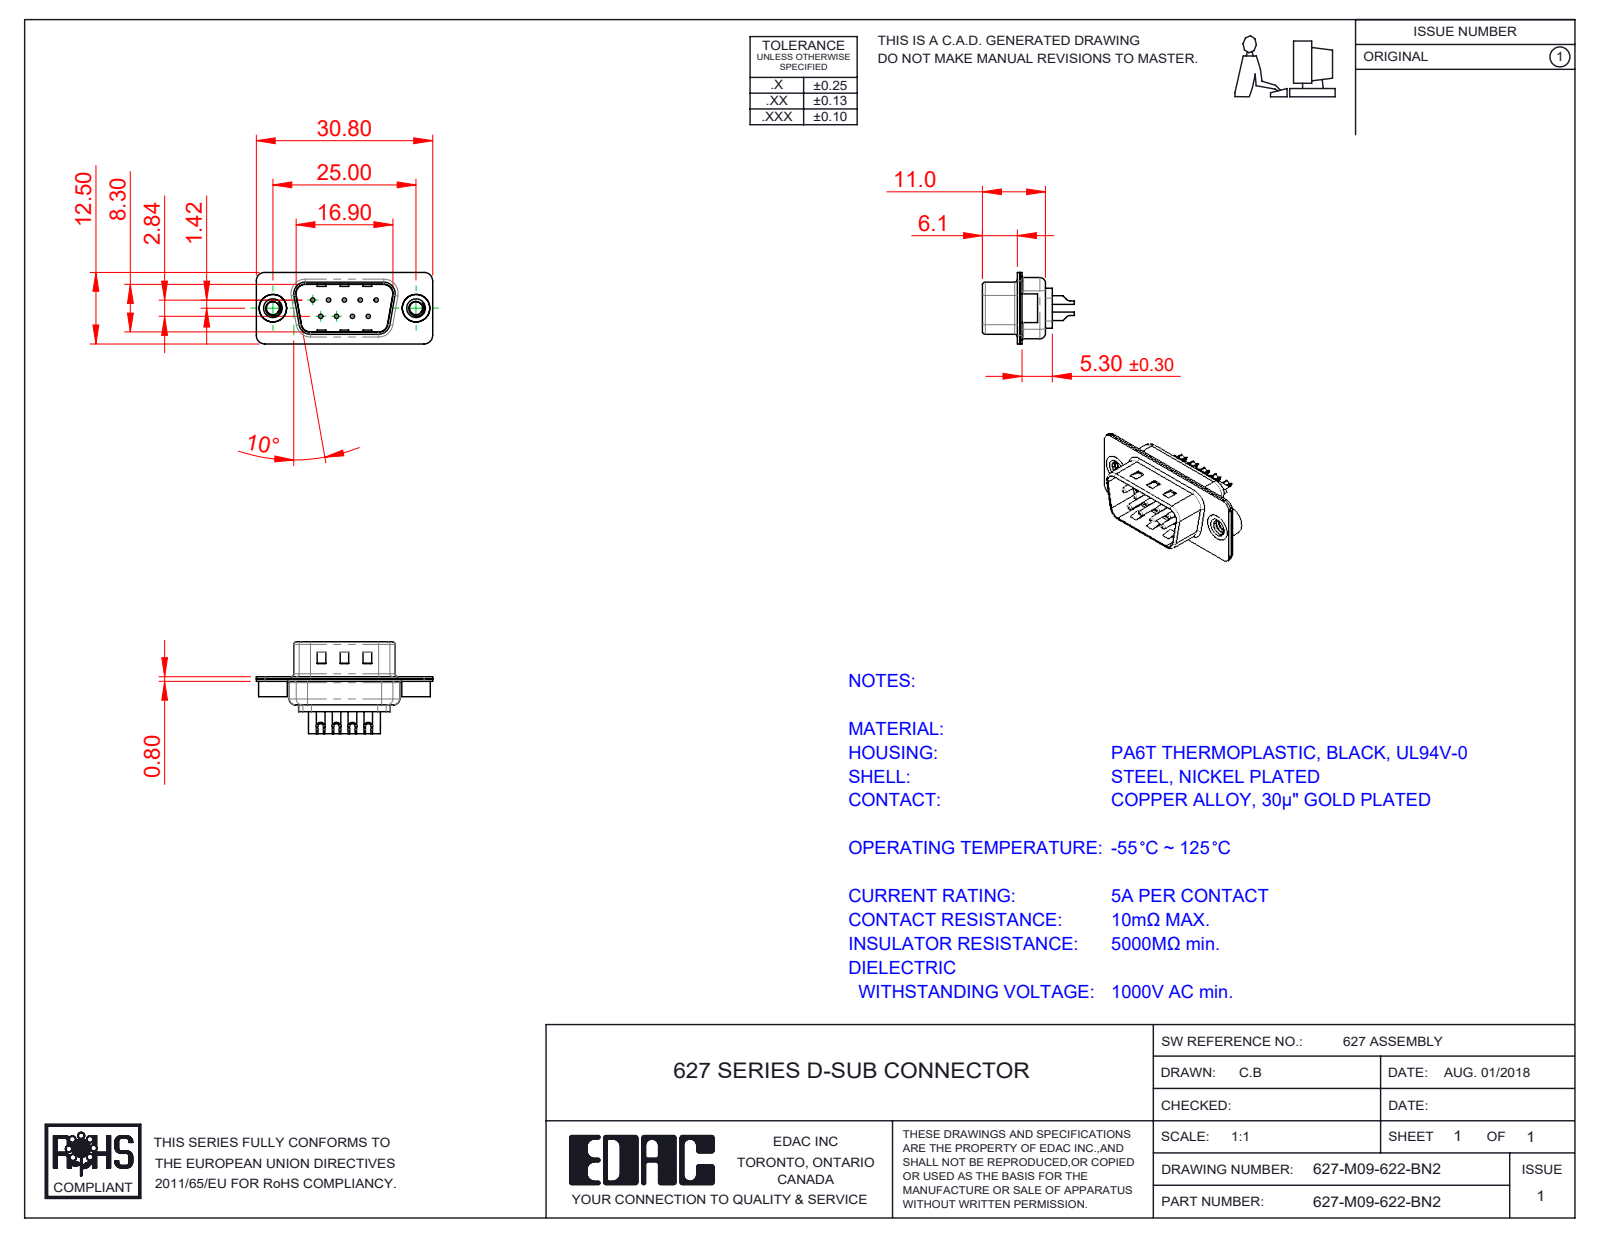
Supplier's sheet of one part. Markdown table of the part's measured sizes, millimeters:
| quantity | value |
| --- | --- |
| part name | 627M Shell Rear_09 Contacts; 627-M09-622-BN2; 627M Contact Row 2_22; 627M Shell Front_09 Contacts (+3 more) |
| STEP written by | SolidWorks 2020 (CONFIG_CONTROL_DESIGN) |
| units | millimeters |
| bodies | 14 solids, 637 faces (188 planar, 273 cylindrical, 176 other) |
| overall size | 30.8 × 16.05 × 12.5 |
| volume | 1 331 mm³ |
| surface area | 3 658 mm² |
| round holes (diameter × count) | 0.75 × 9, 1 × 9, 1.6 × 9, 2 × 9, 2.26 × 2, 4 × 2, 4.8 × 2 |
| round bosses / shafts (diameter × count) | 1.5 × 9, 5 × 2, 4.9 × 2 |
| partial cylindrical surfaces (radius × count) | 1.5 × 16, 2 × 12, 0.5 × 8, 1.6 × 8, 1 × 6, 0.25 × 4, 0.6 × 4, 0.65 × 4 |
| main face-to-face distances | 0.4, 0.8, 9.5, 9.1, 8.7, 0.65, 9.9, 1.2, 0.75, 0.35 |
| hole center spacings | 3.16, 2.77, 5.54, 5.03, 5.04, 8.31, 7.1, 7.48 |
